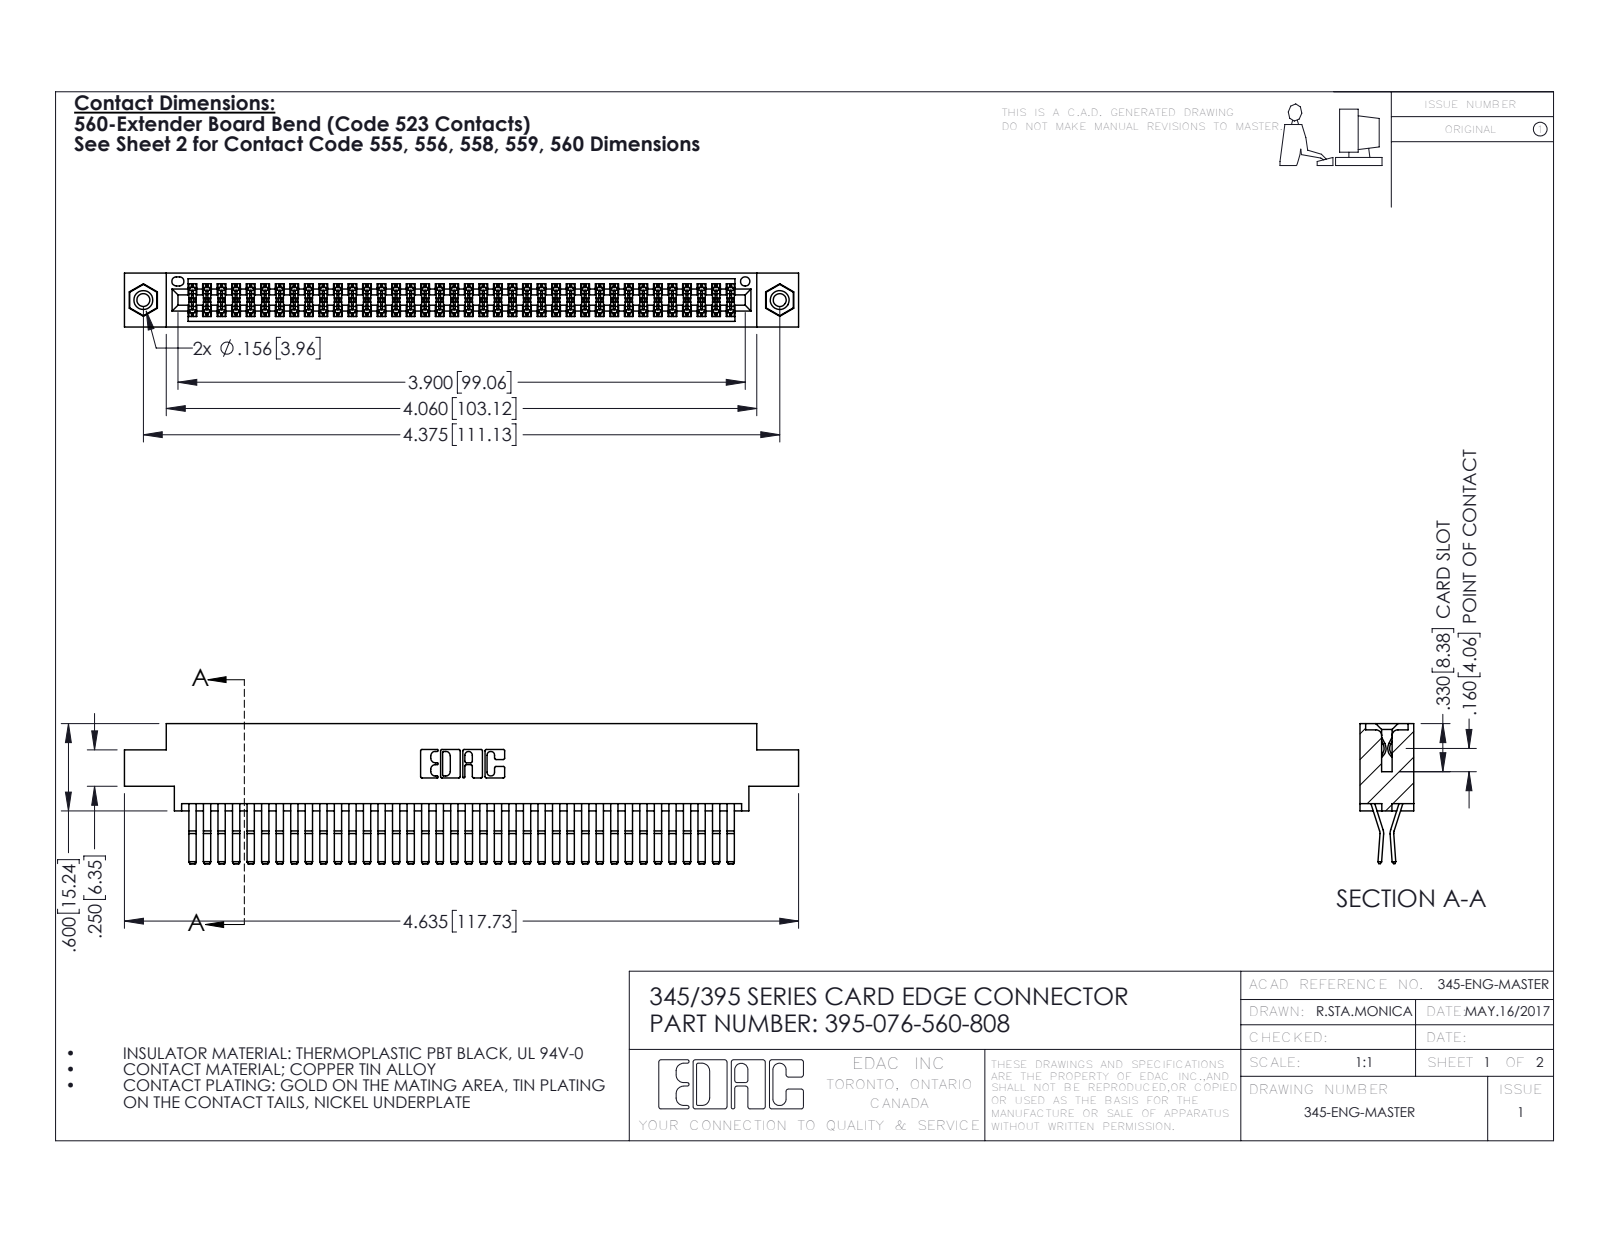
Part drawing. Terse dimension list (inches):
name: 395-076-560-808; 345-292-001_560 Tail; 345 Part_0.170 Offset - 0.156 Dia-TI; 345-250-001_345-250-003-102
written by: SolidWorks 2016 (CONFIG_CONTROL_DESIGN)
unit: in
bodies: 79 solids, 4142 faces (2624 planar, 1502 cylindrical, 16 other)
size: 4.635 × 0.962 × 0.37
volume: 0.719 in³; area: 29.09 in²
holes: 2× ⌀0.089, 2× ⌀0.125, 2× ⌀0.156, 1× ⌀0.064
bosses: 2× ⌀0.155
rounds: 114× R0.006, 22× R0.01, 6× R0.007, 6× R0.031, 3× R0.026, 2× R0.01, 2× R0.014, 2× R0.019
face distances: 0.025, 0.072, 0.298, 0.37, 0.2, 0.098, 0.272, 0.225, 0.175, 0.149
hole spacings: 0.27, 4.139, 4.375
